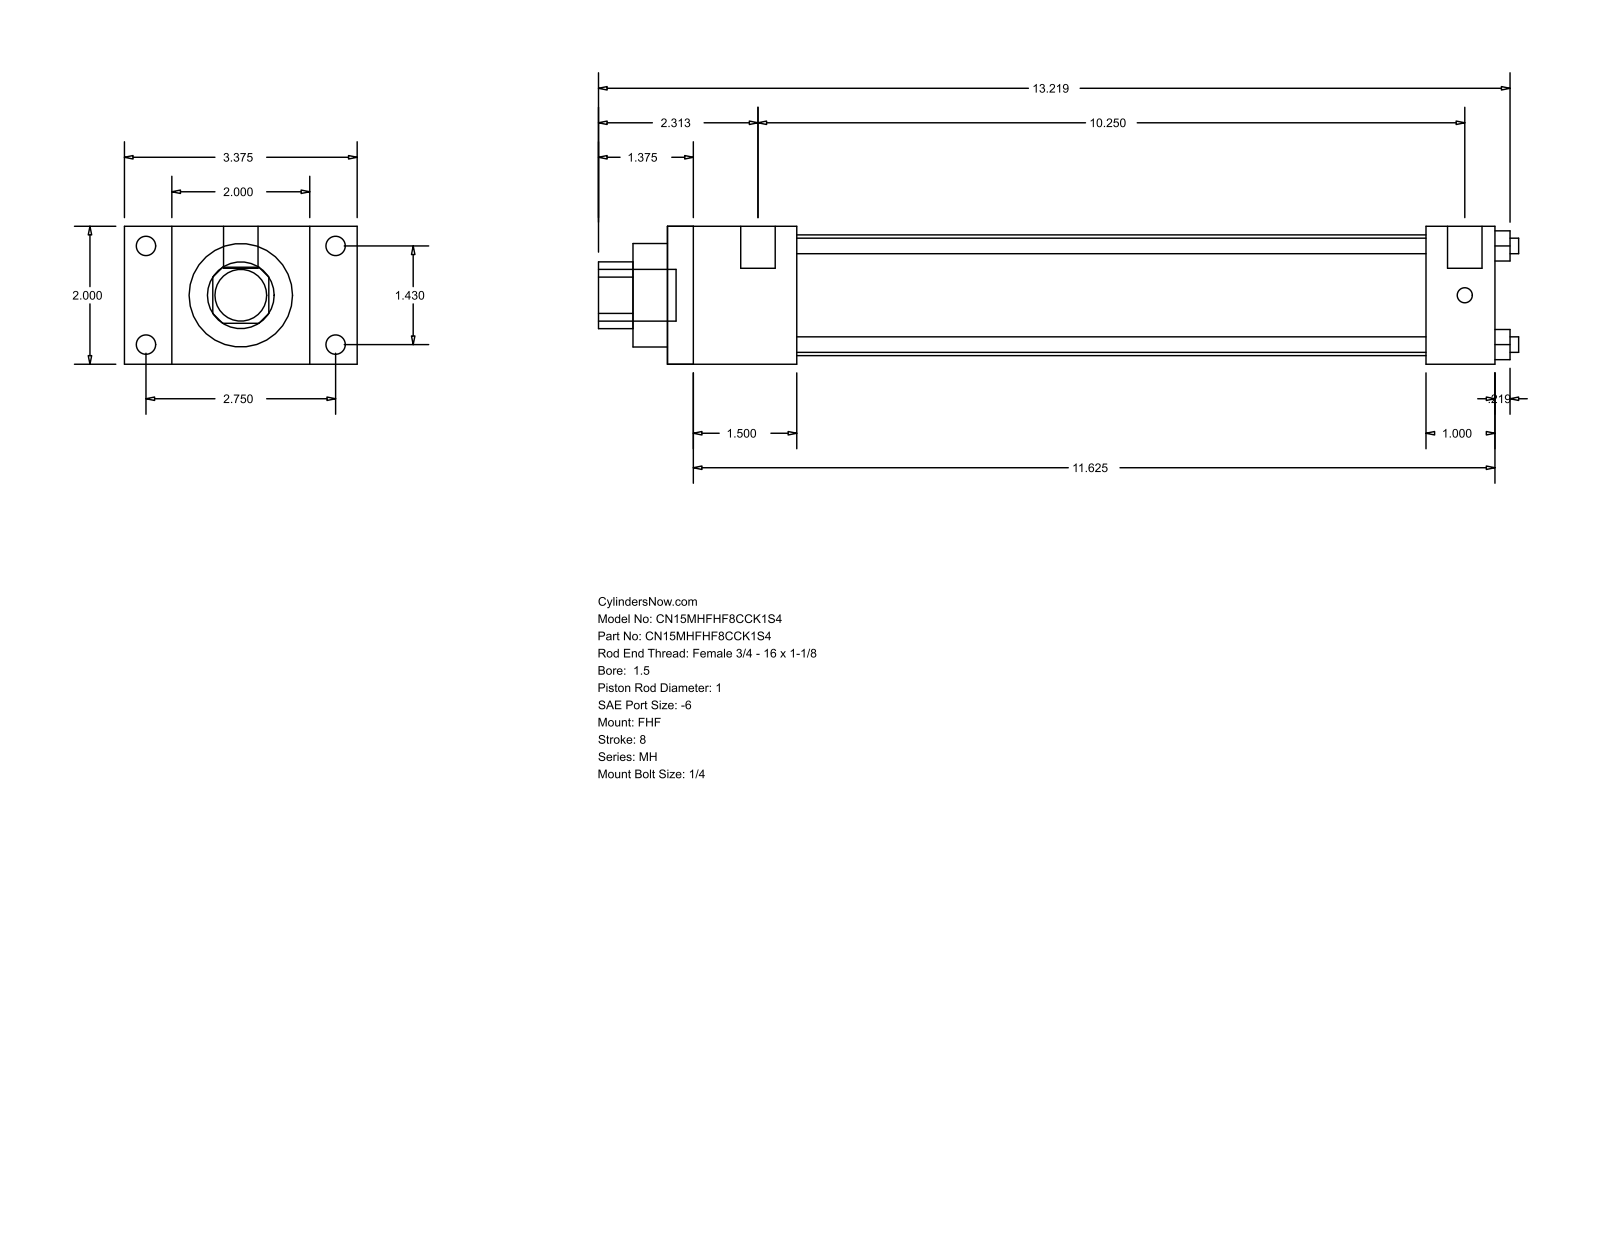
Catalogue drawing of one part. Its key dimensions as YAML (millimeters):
part_name: "MH_FHF__0150_1"
step_written_by: "GSSL Pune (CONFIG_CONTROL_DESIGN)"
units: millimeters
bodies: {solids: 0, faces: 88, planar: 60, cylindrical: 28, other: 0}
overall_size: [338.93, 85.72, 50.8]
round_holes:
  - {diameter: 5.71, count: 4}
  - {diameter: 25.4, count: 1}
  - {diameter: 38.1, count: 1}
  - {diameter: 44.45, count: 1}
round_bosses_or_shafts:
  - {diameter: 7.14, count: 4}
  - {diameter: 5.56, count: 4}
  - {diameter: 12.7, count: 2}
  - {diameter: 19.05, count: 1}
partial_cylinders:
  - {radius: 12.29, count: 1}
face_to_face_distances: [50.8, 17.46, 68.26, 47.63, 85.72, 304.8, 257.17, 25.4, 279.4, 231.77]
hole_center_spacings: [25.68, 36.32, 51.36]
